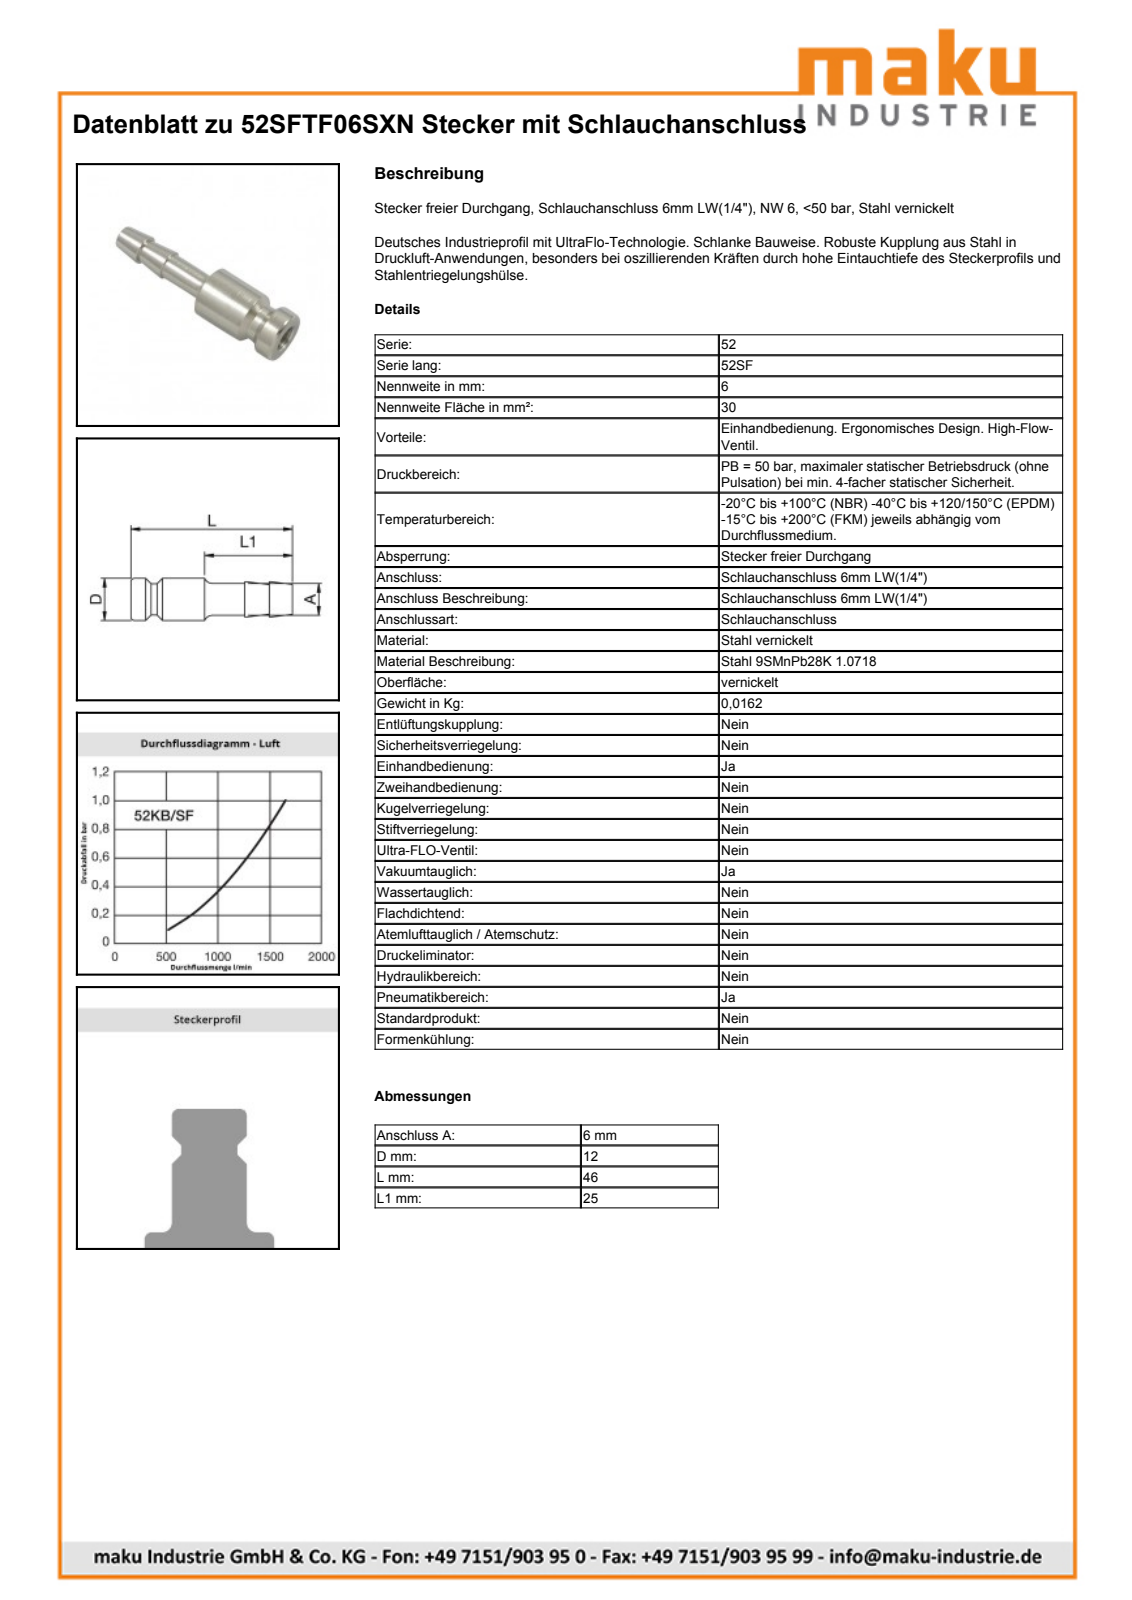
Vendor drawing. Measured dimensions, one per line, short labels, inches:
name: D102768
written by: Autodesk Inventor 2011 (AUTOMOTIVE_DESIGN)
unit: in
bodies: 1 solid, 22 faces (5 planar, 6 cylindrical, 11 other)
size: 1.811 × 0.47 × 0.47
volume: 0.132 in³; area: 3.367 in²
holes: 1× ⌀0.156, 1× ⌀0.236
bosses: 1× ⌀0.47, 1× ⌀0.35, 1× ⌀0.238
face distances: 1.551, 0.26, 1.811, 0.535, 0.276, 1.276, 0.984, 0.724, 0.449, 0.827
